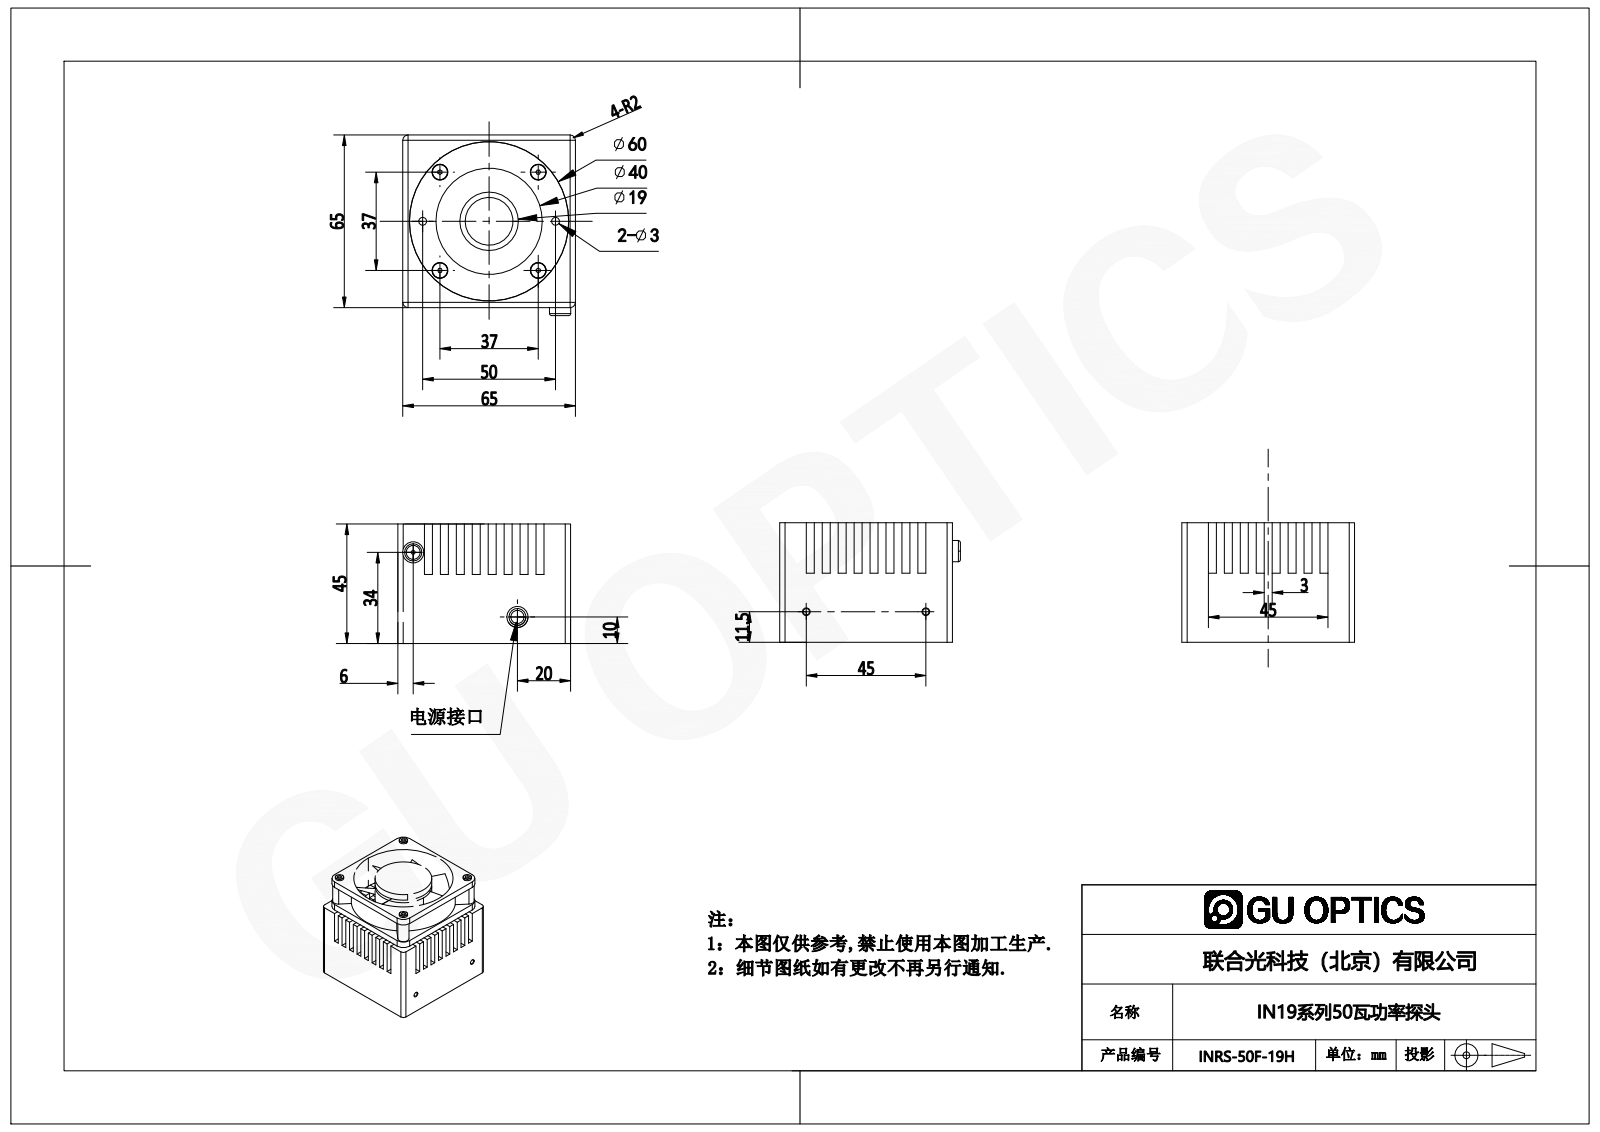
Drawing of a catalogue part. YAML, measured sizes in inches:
part_name: "50W̽ͷ"
step_written_by: "SolidWorks 2020 (CONFIG_CONTROL_DESIGN)"
units: inches
bodies: {solids: 1, faces: 1253, planar: 556, cylindrical: 464, other: 233}
overall_size: [4.946, 3.65, 2.362]
volume: 10.78
surface_area: 109.3
round_holes:
  - {diameter: 0.097, count: 6}
  - {diameter: 0.236, count: 4}
  - {diameter: 0.118, count: 2}
  - {diameter: 0.197, count: 1}
  - {diameter: 0.209, count: 1}
  - {diameter: 0.315, count: 1}
  - {diameter: 0.748, count: 1}
  - {diameter: 1.575, count: 1}
  - {diameter: 2.362, count: 1}
round_bosses_or_shafts:
  - {diameter: 0.039, count: 9}
  - {diameter: 0.232, count: 4}
  - {diameter: 0.197, count: 2}
  - {diameter: 0.118, count: 2}
  - {diameter: 0.11, count: 2}
  - {diameter: 2.358, count: 1}
  - {diameter: 1.181, count: 1}
  - {diameter: 0.315, count: 1}
partial_cylinders:
  - {radius: 0.008, count: 102}
  - {radius: 0.039, count: 16}
  - {radius: 0.004, count: 12}
  - {radius: 0.079, count: 8}
  - {radius: 0.02, count: 4}
  - {radius: 0.157, count: 4}
  - {radius: 0.197, count: 4}
  - {radius: 0.104, count: 2}
face_to_face_distances: [0.118, 0.236, 0.354, 0.472, 0.591, 0.827, 0.709, 0.945, 1.063, 1.181]
hole_center_spacings: [1.754, 0.39, 0.772, 1.004, 1.03, 1.42, 1.457, 1.861]
